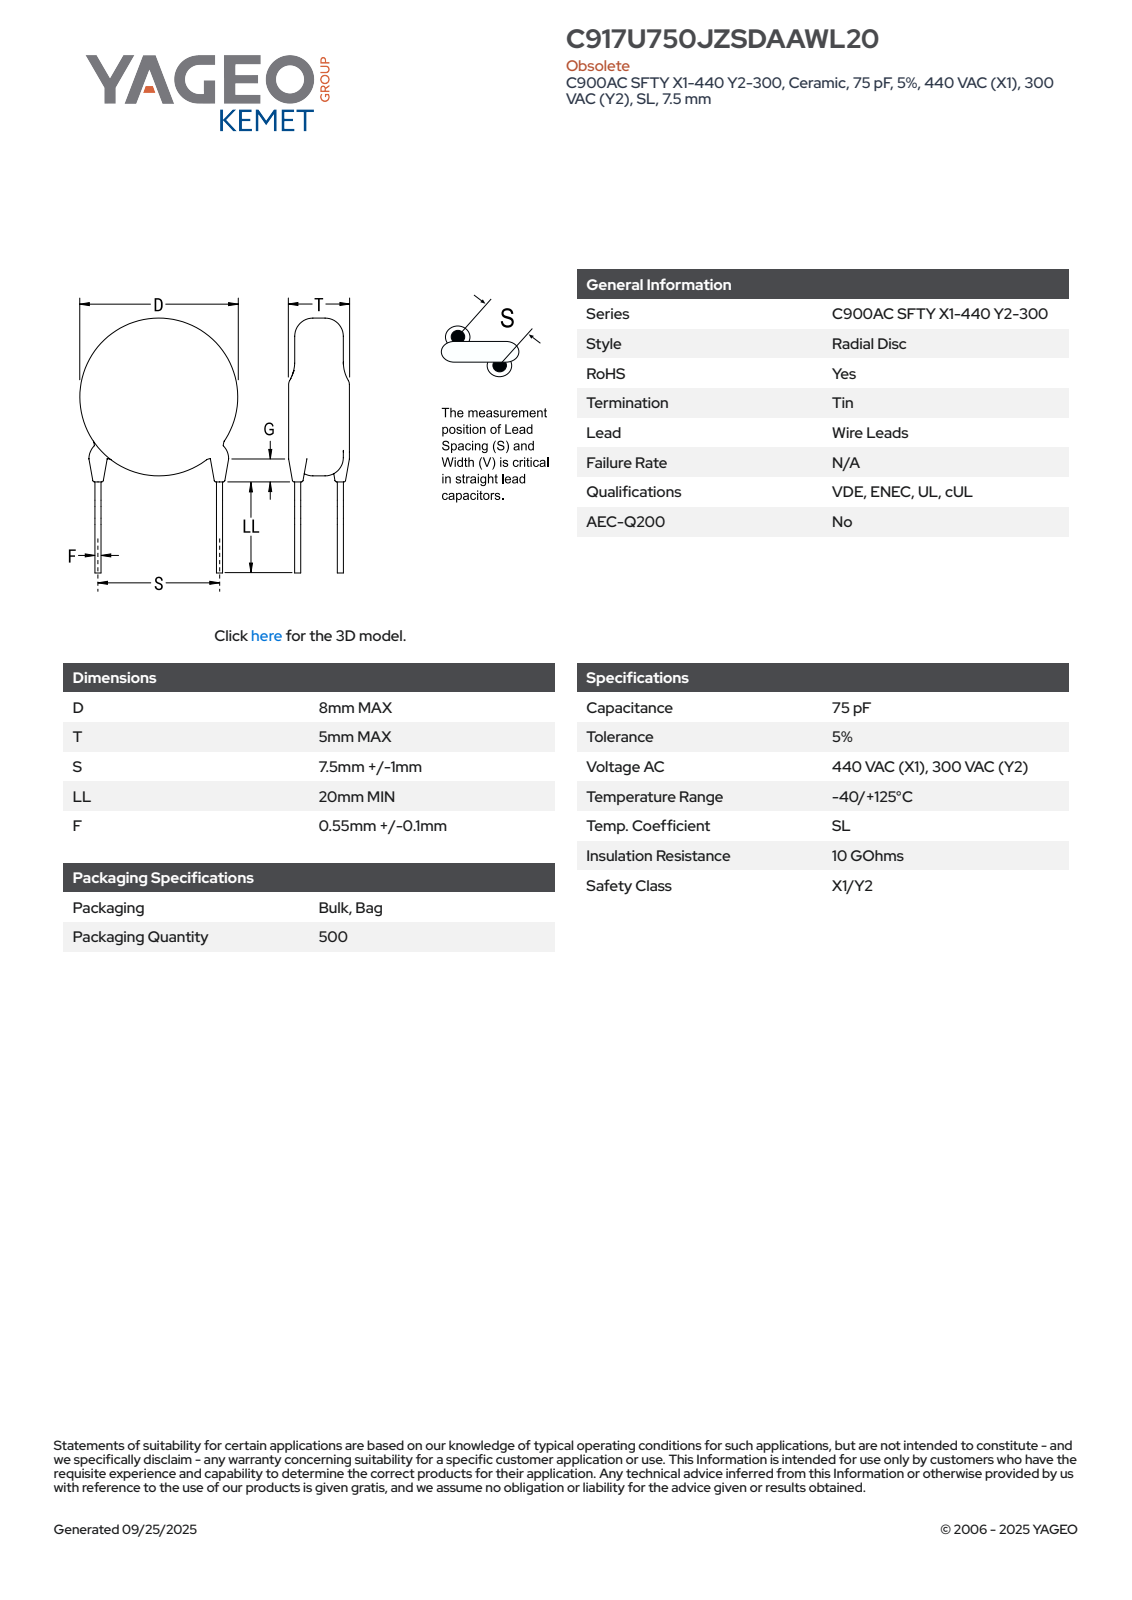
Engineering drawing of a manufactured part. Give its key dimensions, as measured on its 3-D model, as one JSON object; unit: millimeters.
{"part_name": "CCD_STC900_D8T5S7.5LL20F0.65G3", "step_written_by": "SolidWorks 2014 (AUTOMOTIVE_DESIGN)", "units": "millimeters", "bodies": {"solids": 4, "faces": 83, "planar": 61, "cylindrical": 6, "other": 16}, "overall_size": [28.32, 8, 5], "volume_mm3": 257, "surface_area_mm2": 299, "round_bosses_or_shafts": [[0.65, 2], [8, 1]], "face_to_face_distances": [5, 24.78, 23.86, 0.92, 0.4, 1.04, 3.77, 0.57, 2.73, 2.84]}
